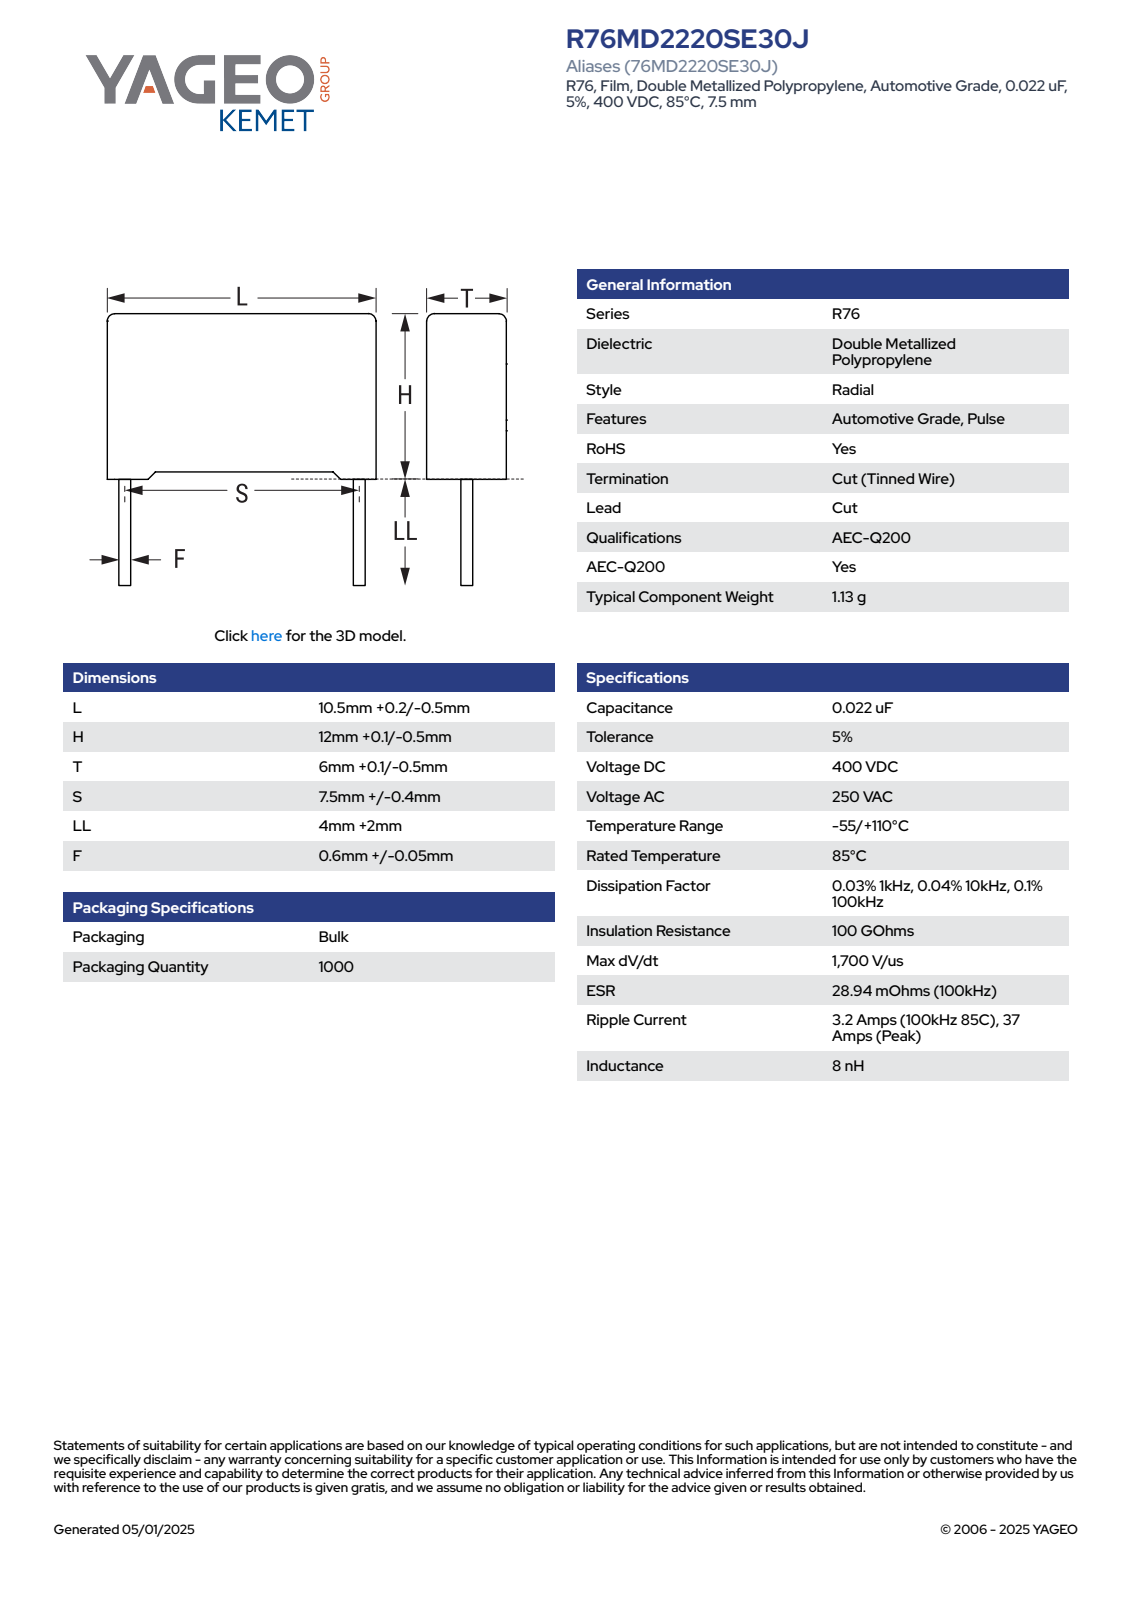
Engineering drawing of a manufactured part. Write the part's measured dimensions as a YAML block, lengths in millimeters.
part_name: "CFR_RB2_10.5X12X6_L10.7H12.1T6.1S7.5LL6F0.65"
step_written_by: "SolidWorks 2021 (AUTOMOTIVE_DESIGN)"
units: millimeters
bodies: {solids: 4, faces: 85, planar: 77, cylindrical: 8, other: 0}
overall_size: [18.1, 10.7, 6.11]
volume: 751
surface_area: 582
round_bosses_or_shafts:
  - {diameter: 0.65, count: 2}
partial_cylinders:
  - {radius: 0.5, count: 4}
face_to_face_distances: [6.1, 10.7, 11.35, 0.36, 5.74, 0.75, 12.1, 10.34, 5.38, 9.98]
